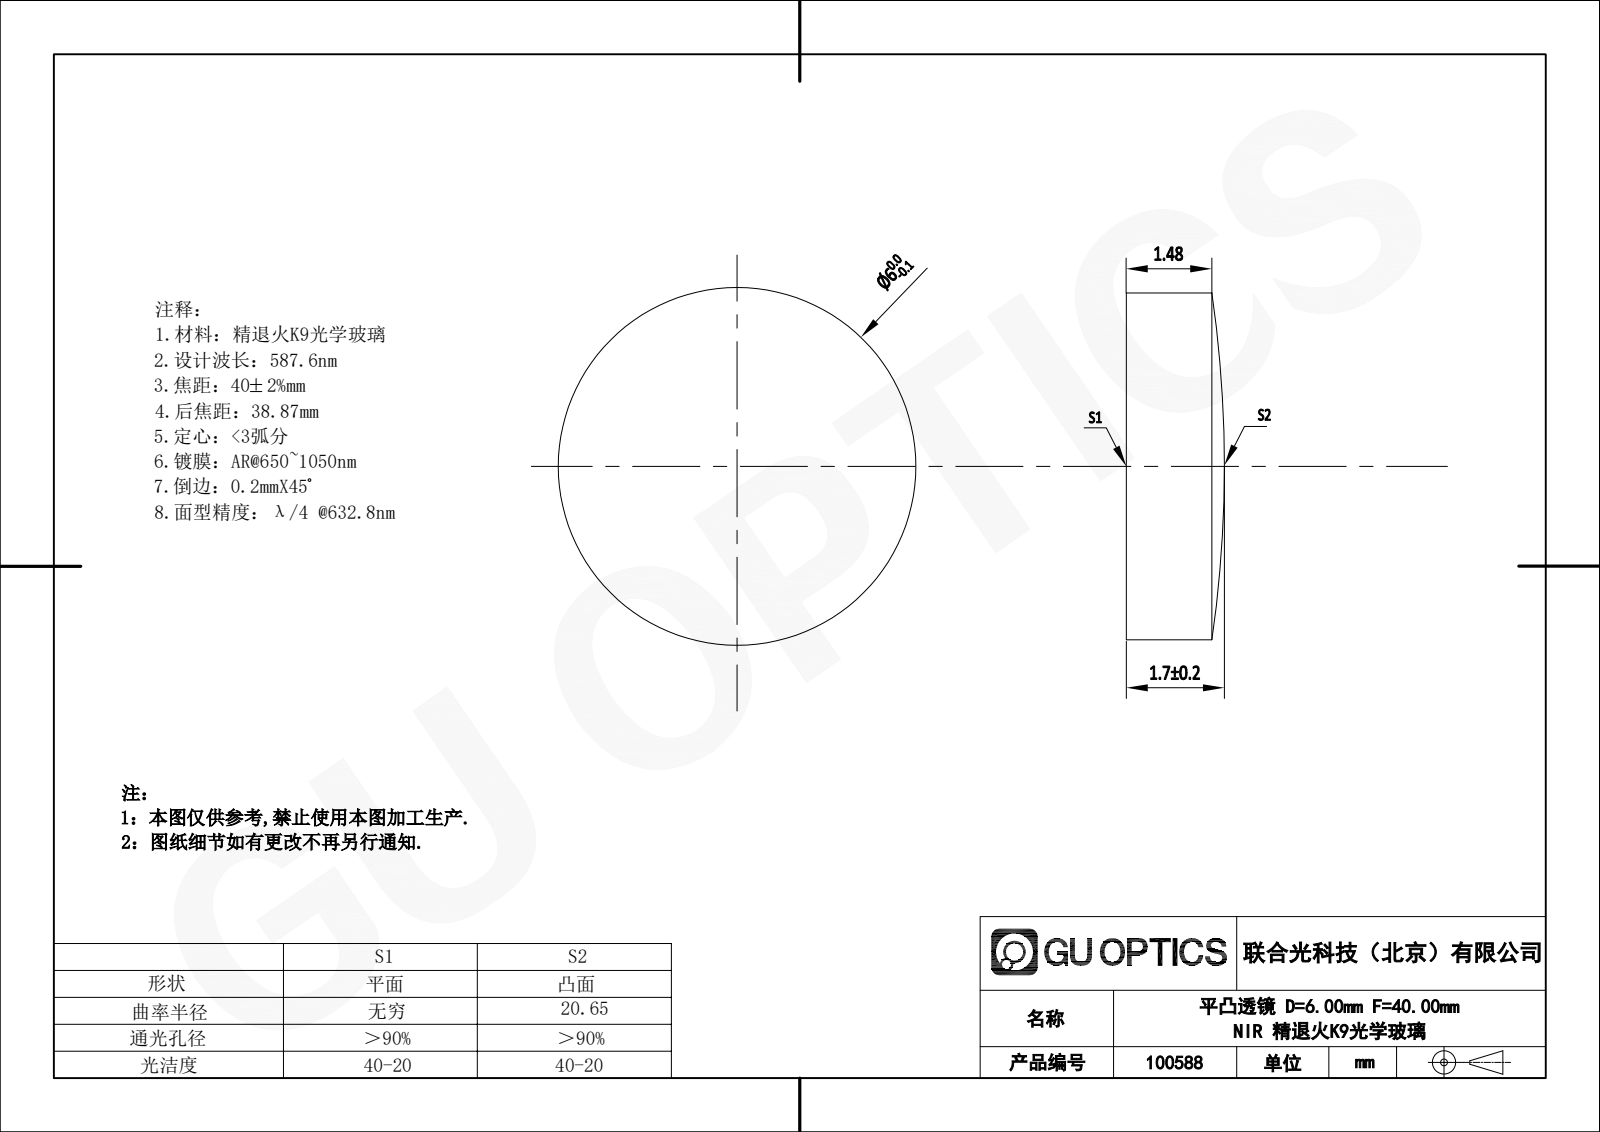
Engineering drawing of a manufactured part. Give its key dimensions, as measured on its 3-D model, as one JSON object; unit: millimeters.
{"part_name": "100588", "step_written_by": "SolidWorks 2020 (CONFIG_CONTROL_DESIGN)", "units": "millimeters", "bodies": {"solids": 1, "faces": 5, "planar": 1, "cylindrical": 2, "other": 2}, "overall_size": [6, 6, 1.7], "volume_mm3": 45, "surface_area_mm2": 85, "round_bosses_or_shafts": [[6, 1]]}
